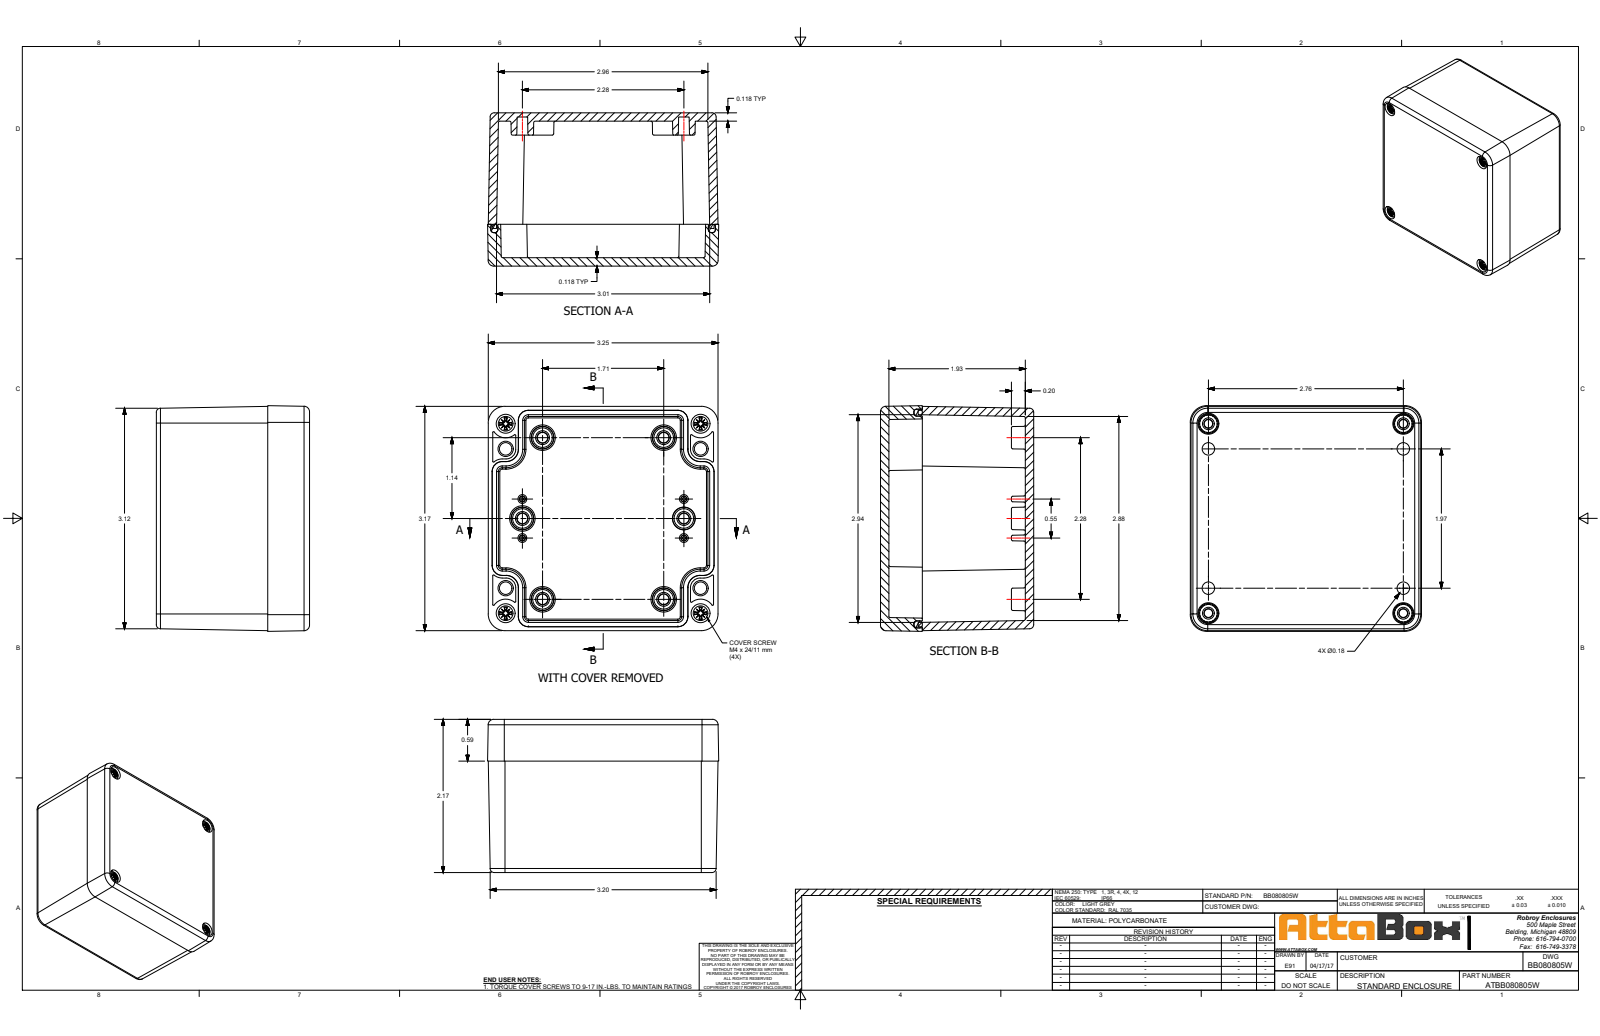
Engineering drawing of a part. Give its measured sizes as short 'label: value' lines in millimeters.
name: BB080805W
written by: SolidWorks 2018 (CONFIG_CONTROL_DESIGN)
unit: mm
bodies: 11 solids, 1672 faces (611 planar, 464 cylindrical, 597 other)
size: 83 × 81 × 55
volume: 105 300 mm³; area: 77 160 mm²
holes: 4× ⌀3.3, 4× ⌀4.5, 4× ⌀4.9, 4× ⌀5, 4× ⌀5.1, 4× ⌀7, 4× ⌀7.3, 4× ⌀7.5
bosses: 4× ⌀6.8, 4× ⌀4.4, 4× ⌀4, 4× ⌀3.3
rounds: 32× R1, 24× R0.3, 16× R0.5, 12× R5, 8× R2.5, 4× R1.5, 4× R2, 4× R2.6
face distances: 3, 52, 55, 49, 40, 9.4, 12, 37, 15, 80.7
hole spacings: 9, 59, 70, 70.6, 91.5, 50, 68, 86
